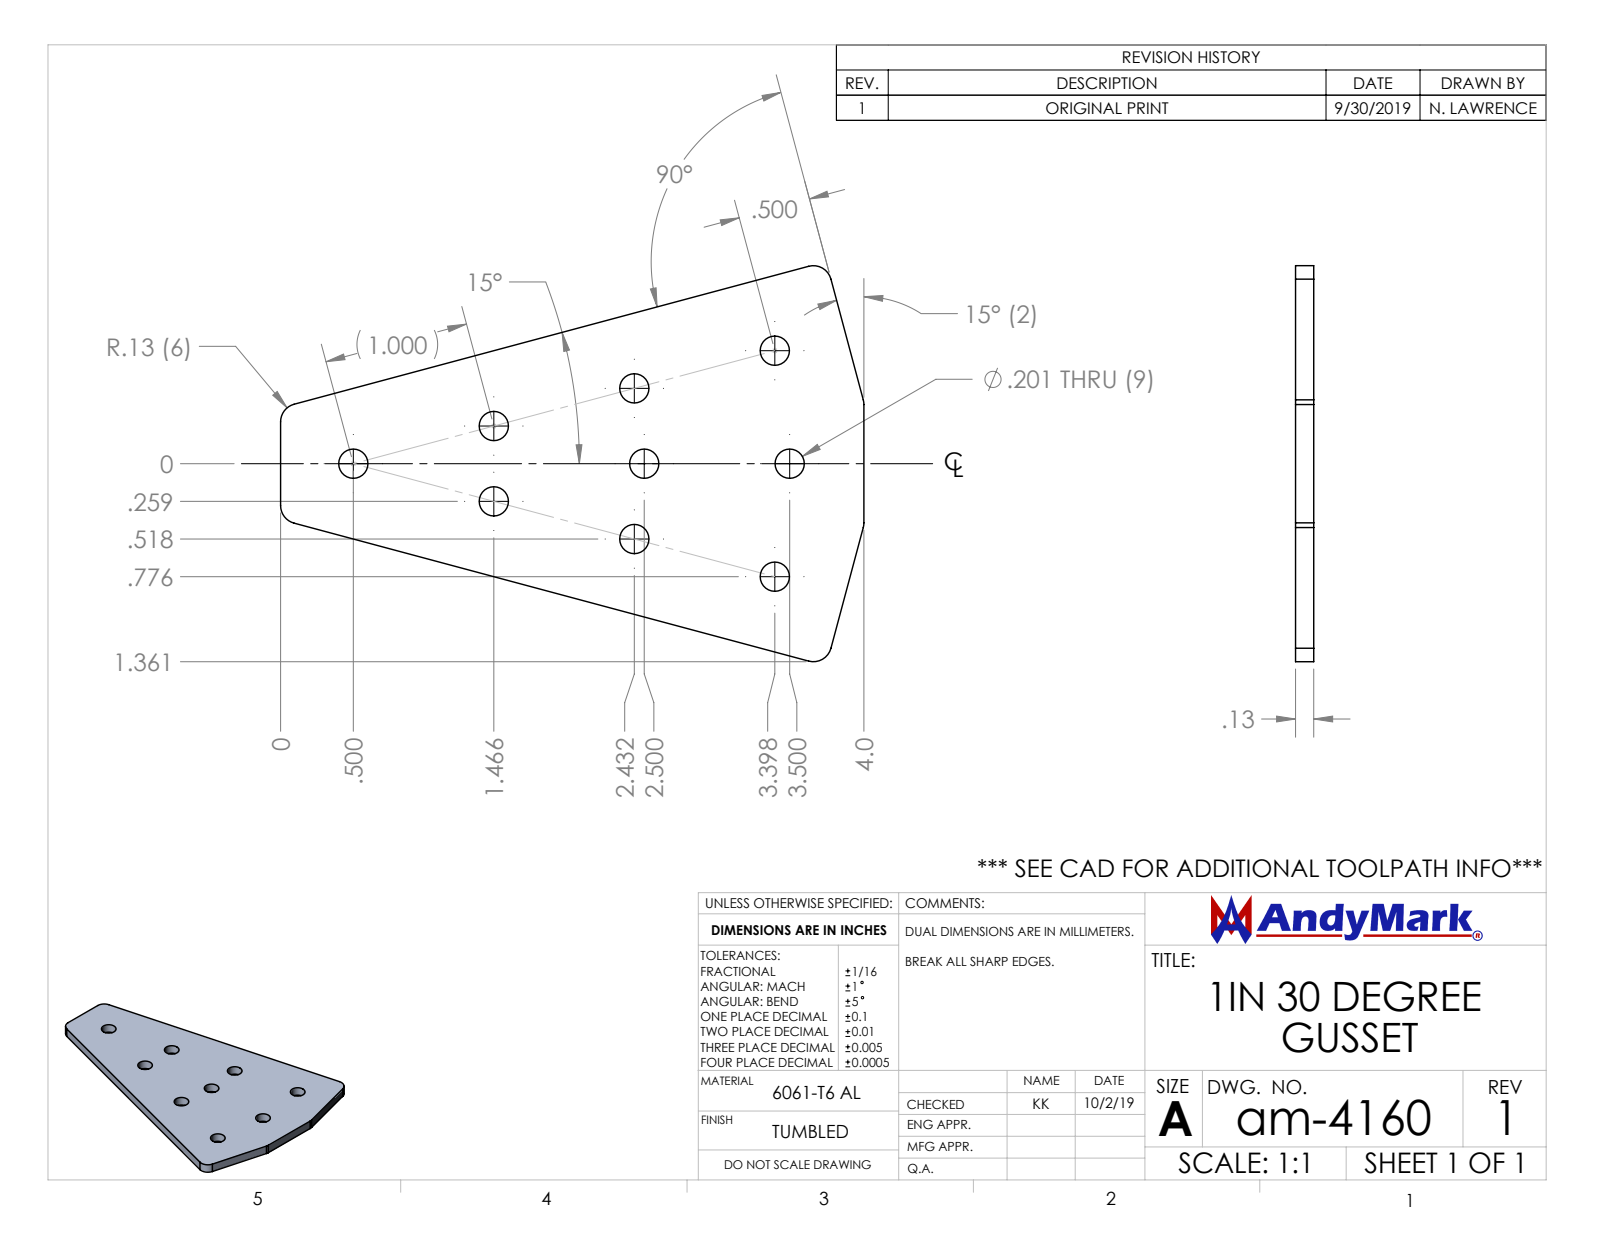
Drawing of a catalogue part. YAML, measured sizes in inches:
part_name: "am-4160 1IN 30deg Gusset"
step_written_by: "SolidWorks 2019 (AUTOMOTIVE_DESIGN)"
units: inches
bodies: {solids: 1, faces: 23, planar: 8, cylindrical: 15, other: 0}
overall_size: [4.01, 2.721, 0.125]
volume: 0.853
surface_area: 15.76
round_holes:
  - {diameter: 0.201, count: 9}
partial_cylinders:
  - {radius: 0.125, count: 6}
face_to_face_distances: [0.125, 4.01]
hole_center_spacings: [2, 1, 3, 0.522, 0.783, 1, 1.066, 1.187]
